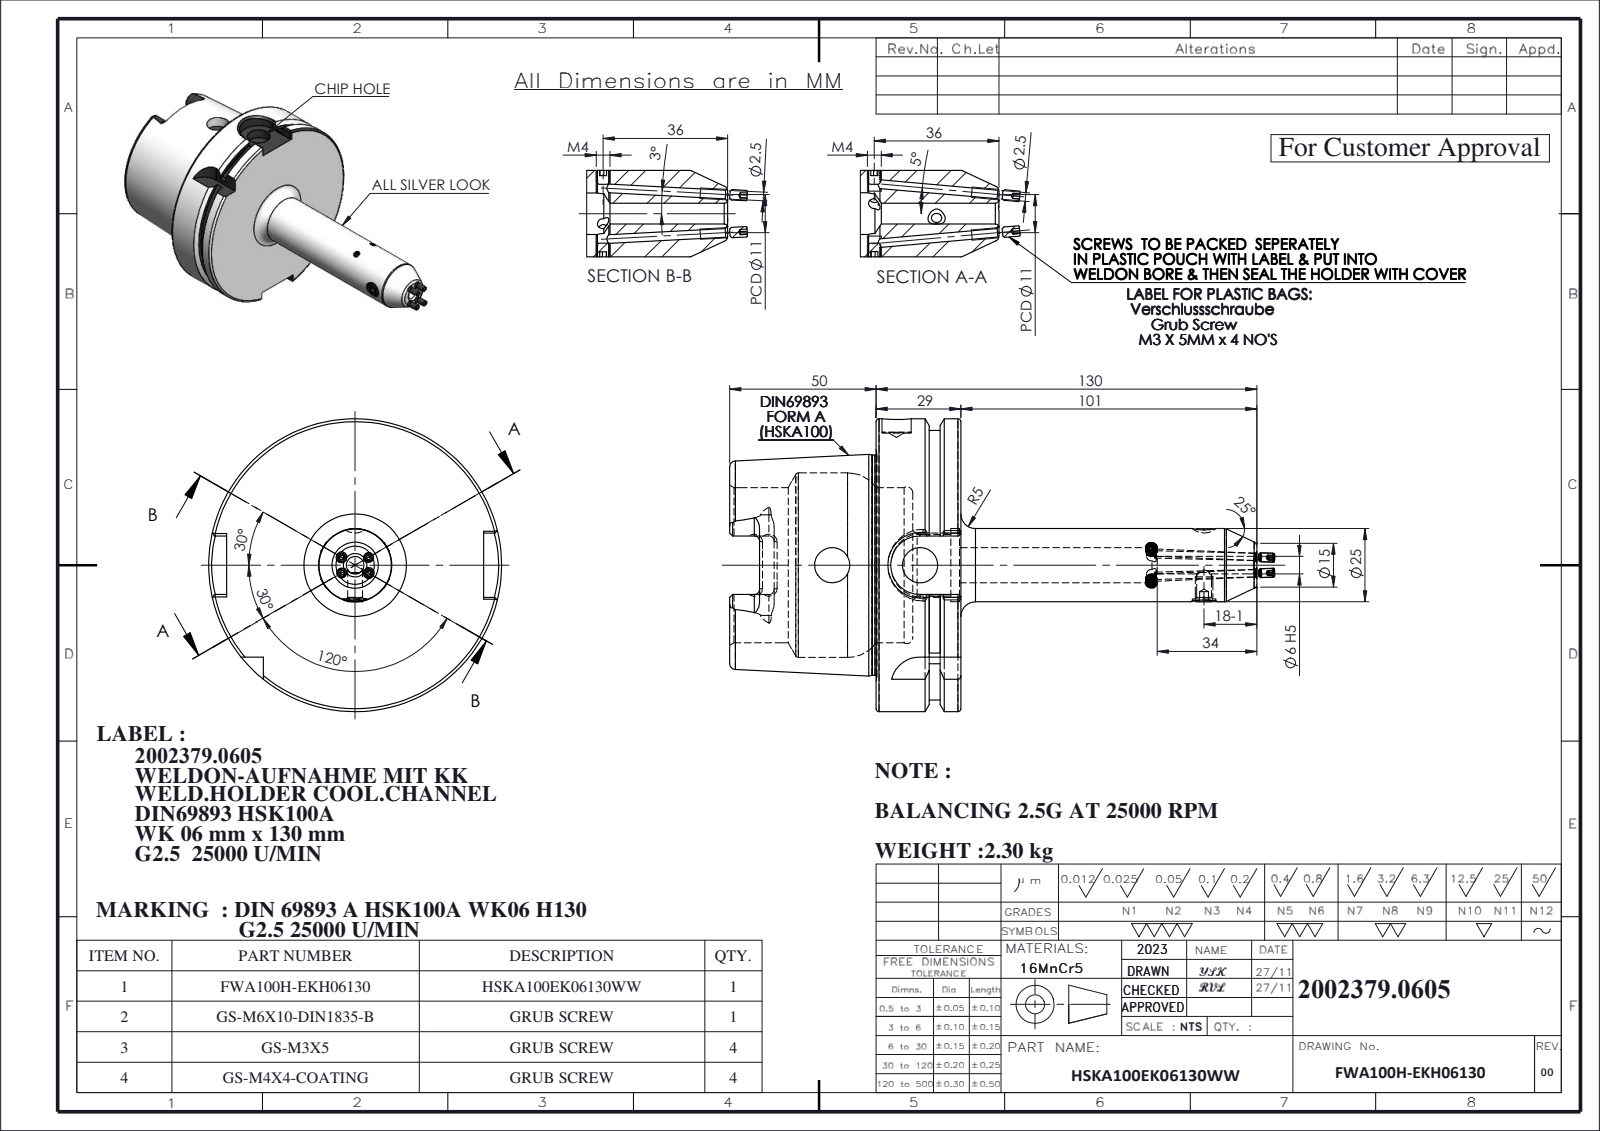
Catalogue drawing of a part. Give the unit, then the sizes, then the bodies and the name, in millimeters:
Units: millimetres
Overall size (bounding box): 186.13 × 100 × 100
Round holes (diameter × count): ⌀2.5 ×4, ⌀12 ×3, ⌀3.3 ×2, ⌀5 ×1, ⌀6 ×1, ⌀8 ×1, ⌀10 ×1, ⌀21 ×1, ⌀25 ×1, ⌀53 ×1, ⌀63 ×1
Round bosses / shafts (diameter × count): ⌀3 ×4, ⌀4 ×2, ⌀100 ×1, ⌀92 ×1, ⌀75.16 ×1, ⌀6 ×1
Partial cylindrical surfaces — rounded edges, fillets, slot ends (radius × count): R1.8 ×6, R4.88 ×4, R10 ×2, R11 ×1
Main face-to-face distances: 28.95, 12.5, 16.45, 50, 62.5, 78.95, 71.88, 21.88, 9.38, 7.07
Hole centre spacings: 30, 105
Volume: 292 694 mm³ · Surface area: 62 607 mm²
Bodies: 10 solids, 511 faces (161 planar, 120 cylindrical, 230 other)
Part name (STEP PRODUCT): HSKA100EK06130WW; GS-M4X4_DIN 913 - M4 x 4-N; GS-M6X10-DIN1835-B; FWA100H-EKH06130 (+1 more)
STEP written by: SolidWorks 2023 (CONFIG_CONTROL_DESIGN)
